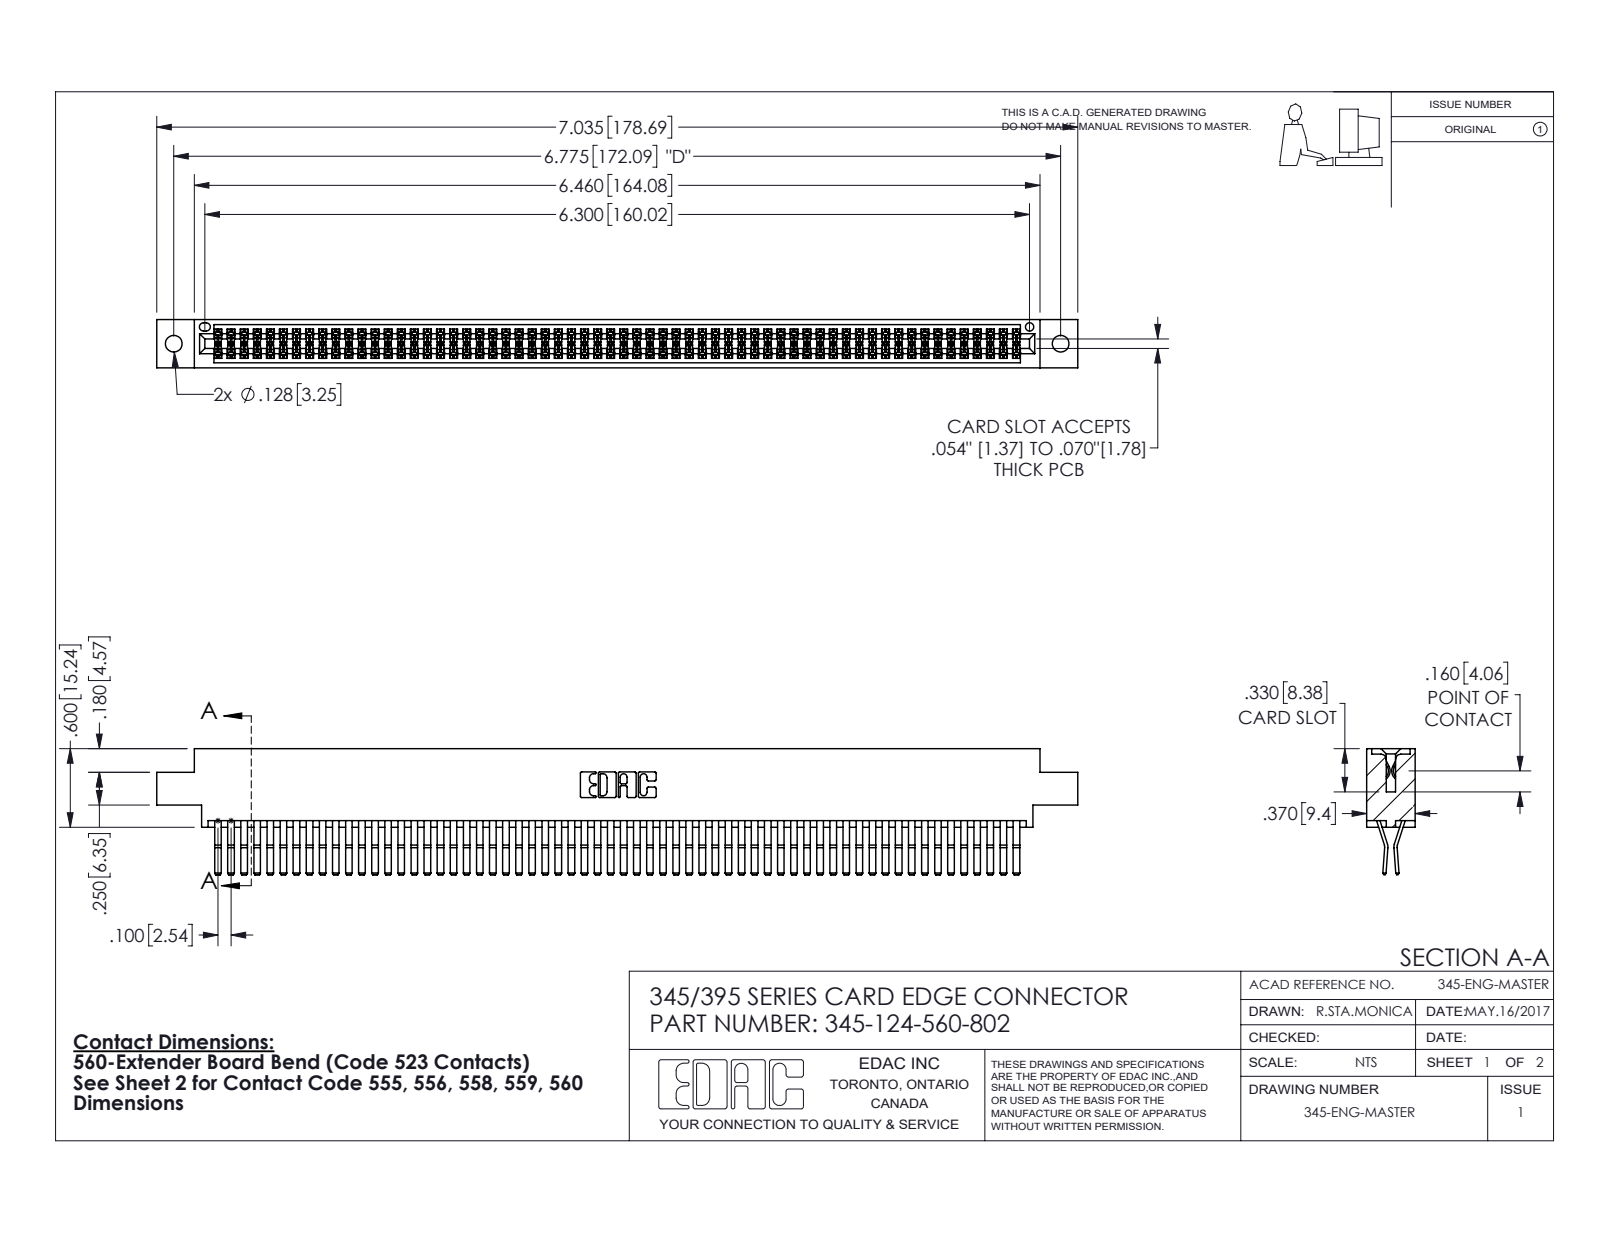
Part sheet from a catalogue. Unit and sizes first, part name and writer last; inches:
Units: inches
Overall size (bounding box): 7.035 × 0.962 × 0.37
Round holes (diameter × count): ⌀0.128 ×2, ⌀0.064 ×1
Partial cylindrical surfaces — rounded edges, fillets, slot ends (radius × count): R0.006 ×186, R0.01 ×22, R0.007 ×6, R0.031 ×6, R0.026 ×3, R0.01 ×2, R0.014 ×2, R0.019 ×2
Main face-to-face distances: 0.025, 0.298, 0.072, 0.37, 0.2, 0.098, 0.272, 0.225, 0.175, 0.149
Hole centre spacings: 0.27, 6.539, 6.775
Volume: 1.111 in³ · Surface area: 45.35 in²
Bodies: 125 solids, 6578 faces (4176 planar, 2402 cylindrical, 0 other)
Part name (STEP PRODUCT): 345 Part_0.170 Offset - 0.128 Dia; 345-124-560-802; 345-292-001_560 Tail
STEP written by: SolidWorks 2016 (CONFIG_CONTROL_DESIGN)
